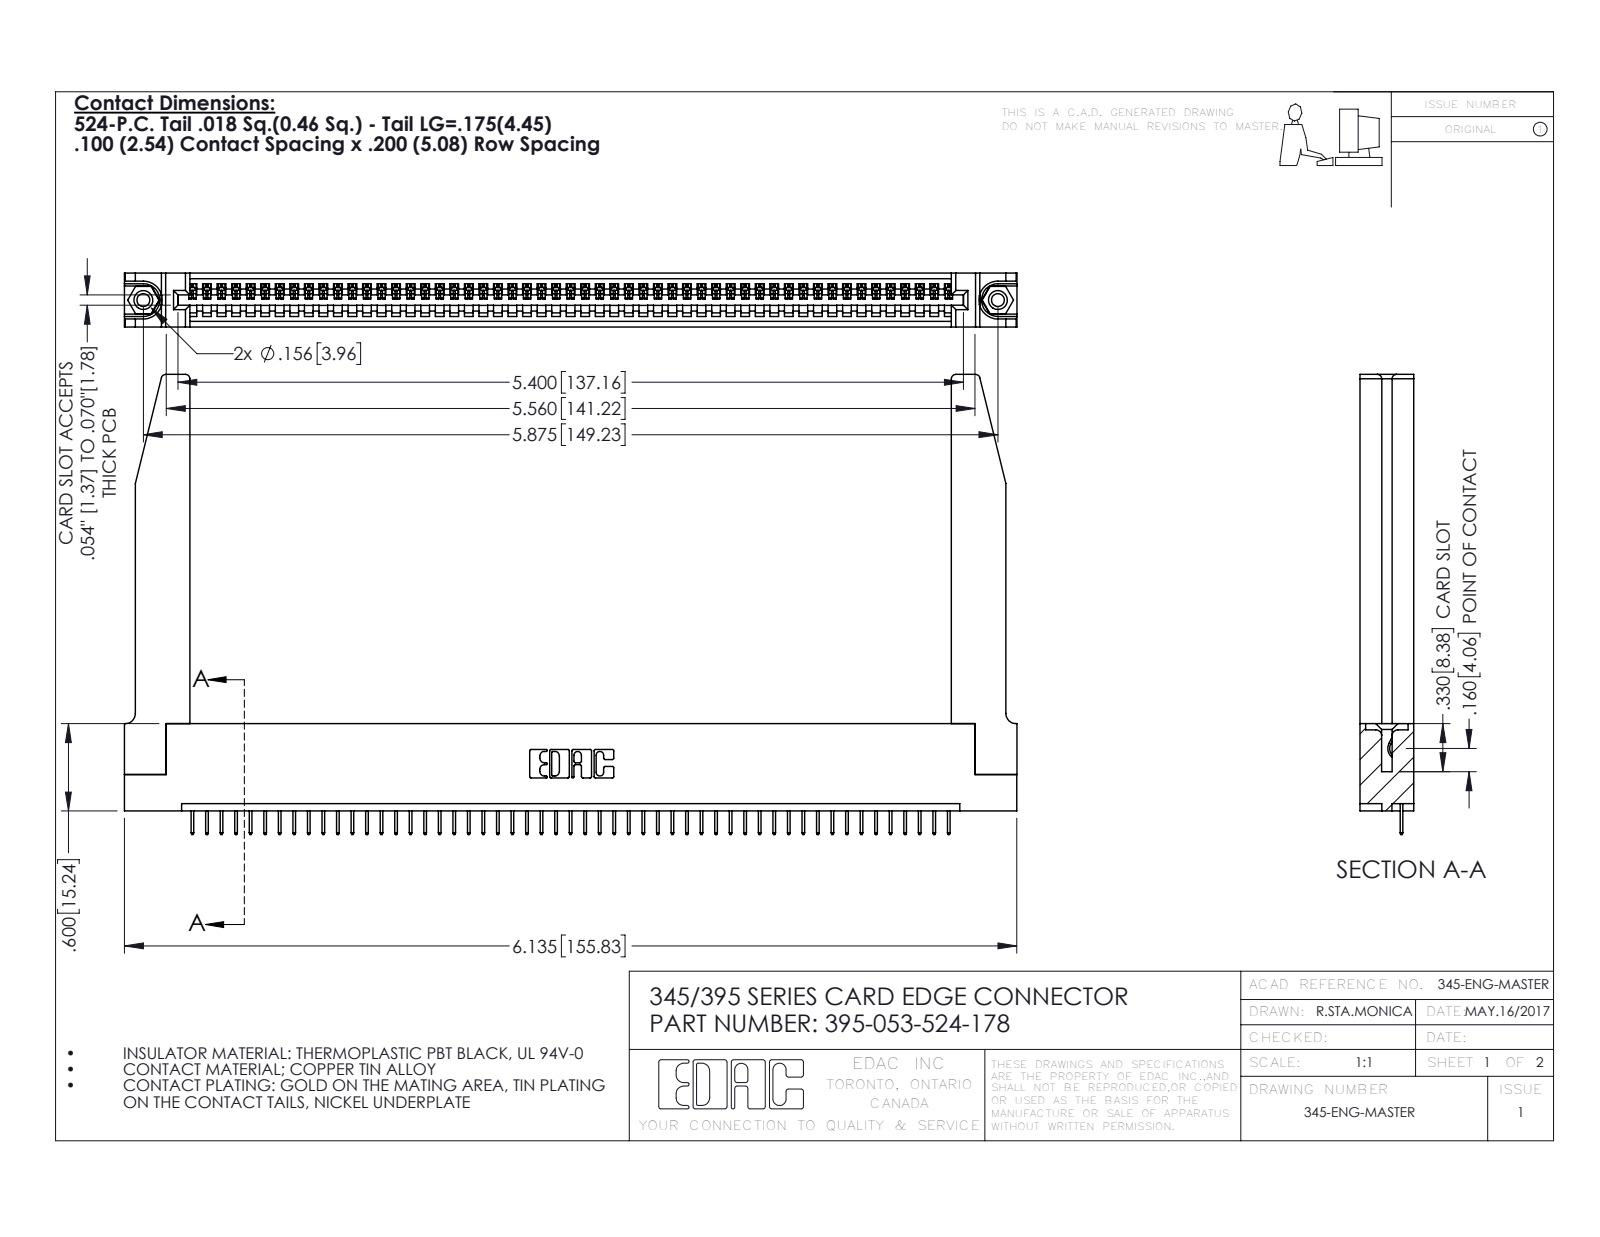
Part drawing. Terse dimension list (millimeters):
name: 345-250-001_345-250-001-102; 345-292-001_345-293-124; 345 Part_Flush Mounting Lugs - 0.156 Dia-TH; 395-053-524-178 (+1 more)
written by: SolidWorks 2016 (CONFIG_CONTROL_DESIGN)
unit: mm
bodies: 58 solids, 3646 faces (2660 planar, 934 cylindrical, 52 other)
size: 155.9 × 80.3 × 9.4
volume: 22 450 mm³; area: 25 840 mm²
holes: 2× ⌀2.3, 2× ⌀3.2, 2× ⌀4, 1× ⌀1.6
bosses: 2× ⌀3.9
rounds: 106× R0.2, 22× R0.3, 8× R0.8, 6× R0.2, 6× R0.8, 3× R0.7, 2× R0.8, 2× R1
face distances: 9.4, 1.8, 7.6, 5.1, 2.5, 6.9, 0.6, 5.7, 3.8, 3.8
hole spacings: 6.9, 143.2, 149.2
